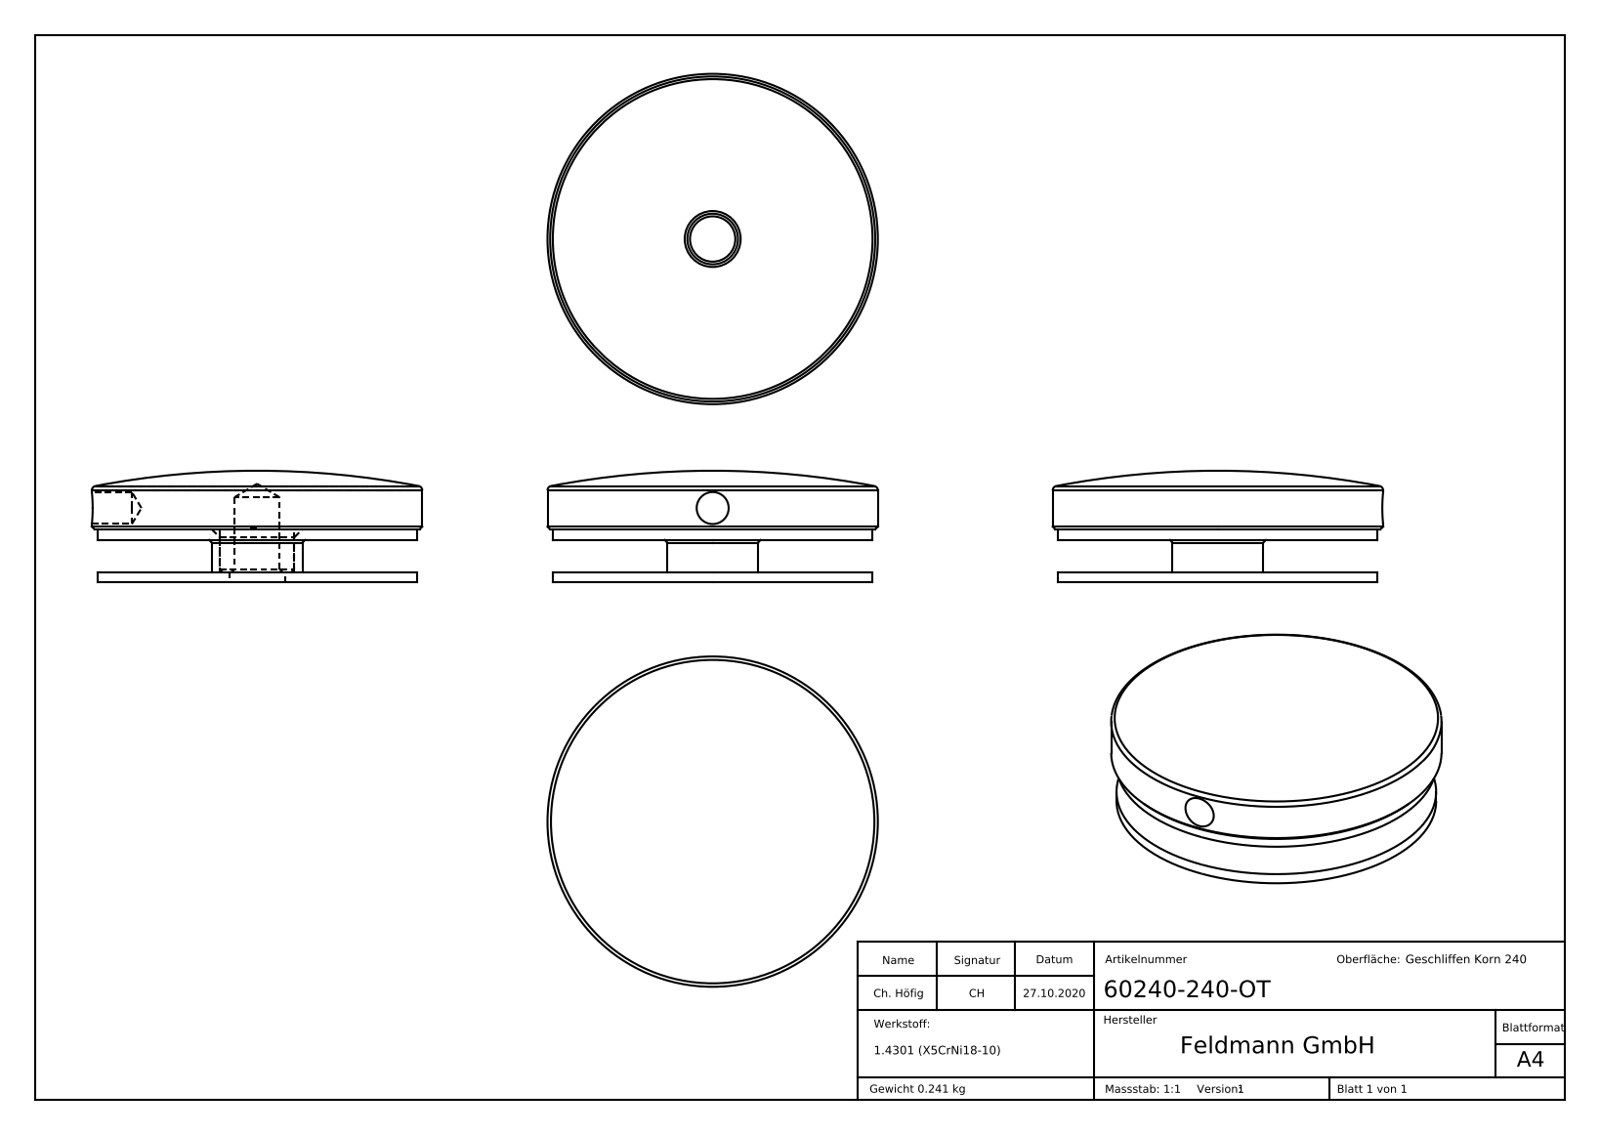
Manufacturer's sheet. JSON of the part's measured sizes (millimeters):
{"part_name": "60240-240-OT Teil3; 60240-240-OT Teil2; 60240-240-OT Teil1; 60240-240-OT (+3 more)", "step_written_by": "SolidWorks 2018 (CONFIG_CONTROL_DESIGN)", "units": "millimeters", "bodies": {"solids": 3, "faces": 288, "planar": 148, "cylindrical": 18, "other": 122}, "overall_size": [62, 62, 21], "volume_mm3": 40026, "surface_area_mm2": 20665, "round_holes": [[6, 1], [8.5, 1], [10.5, 1], [14, 1]], "round_bosses_or_shafts": [[62, 1], [60, 1], [17, 1]], "face_to_face_distances": [8, 2, 10, 6, 10.1, 8.1, 2.1, 3.66, 0.44, 39.66]}
